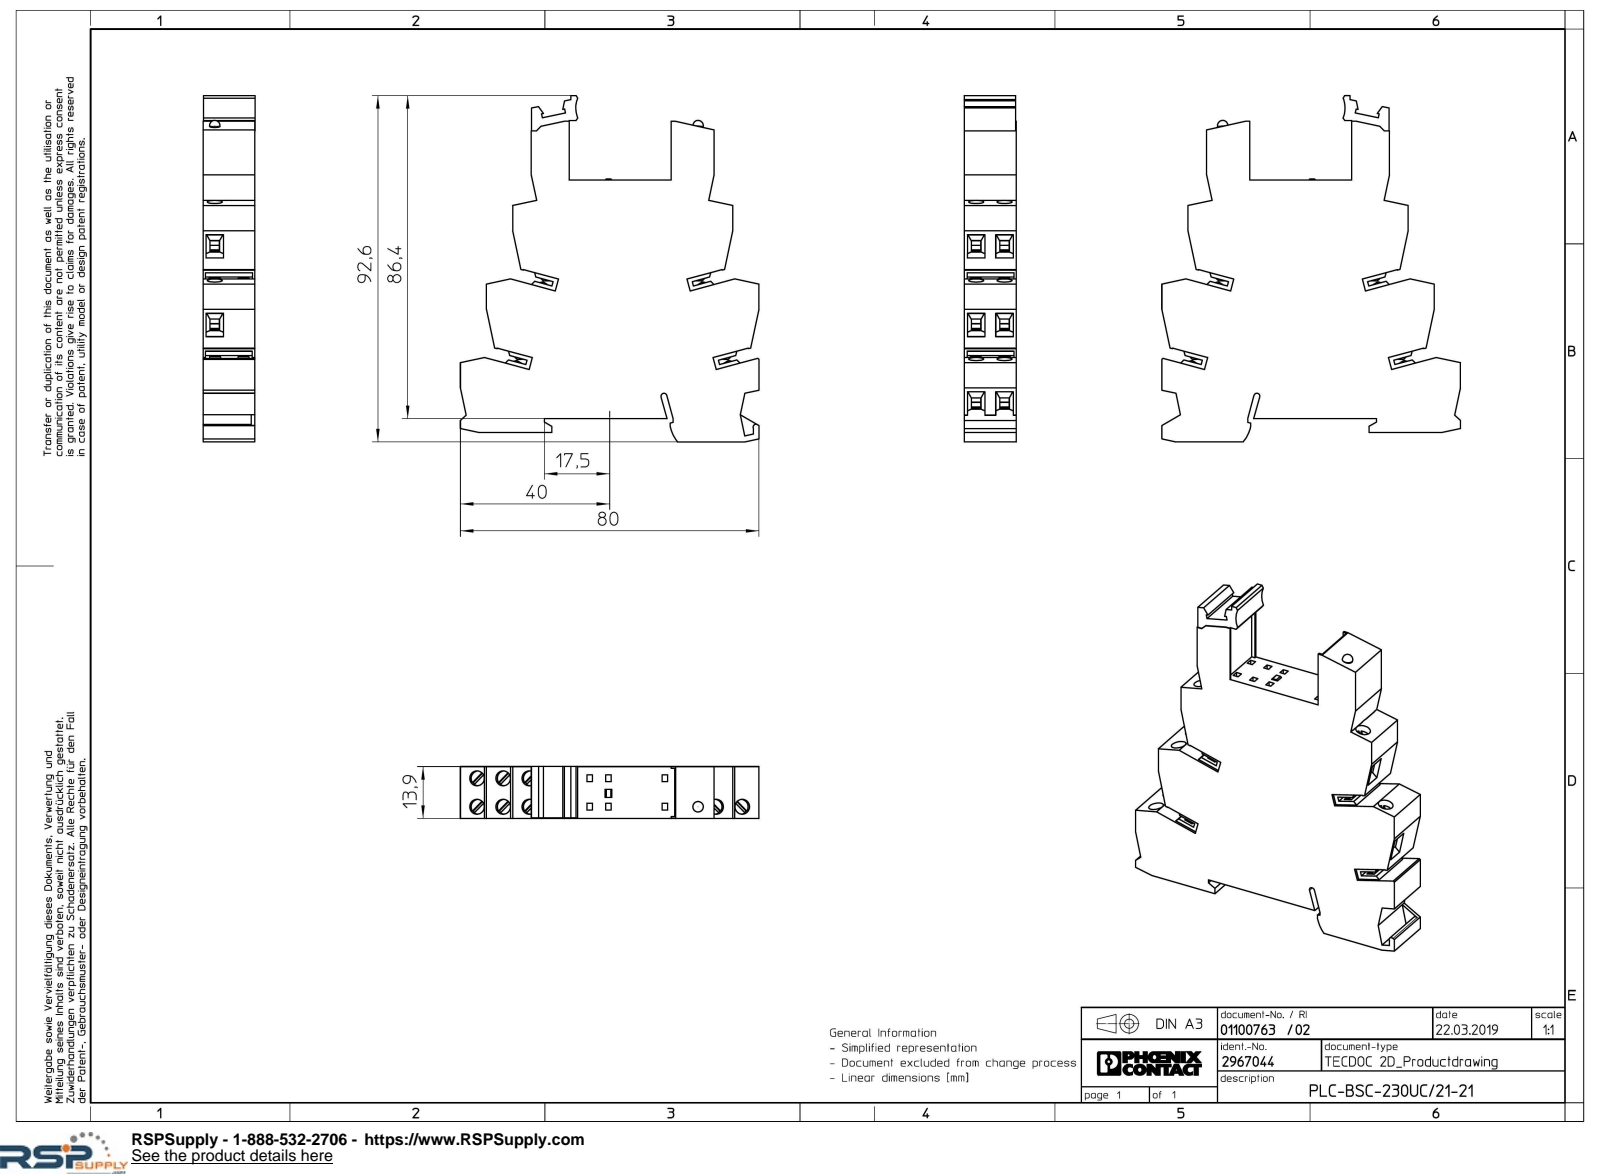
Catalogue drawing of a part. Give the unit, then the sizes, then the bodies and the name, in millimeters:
Units: millimetres
Overall size (bounding box): 92.6 × 80 × 13.95
Round bosses / shafts (diameter × count): ⌀2.8 ×1
Partial cylindrical surfaces — rounded edges, fillets, slot ends (radius × count): R0.8 ×2, R7 ×1, R9.5 ×1
Main face-to-face distances: 13.9, 1.05, 12, 63.8, 22.1, 2.5, 19.08, 7, 2.25, 3.7
Volume: 63 845 mm³ · Surface area: 17 674 mm²
Bodies: 1 solid, 464 faces (441 planar, 6 cylindrical, 17 other)
Part name (STEP PRODUCT): PLC-BSC-14-ACT-Sockel-select
STEP written by: Creo Elements/Direct Modeling 20.1A 29-Sep-2018 (C) Parametric Technology GmbH (AUTOMOTIVE_DESIGN)
